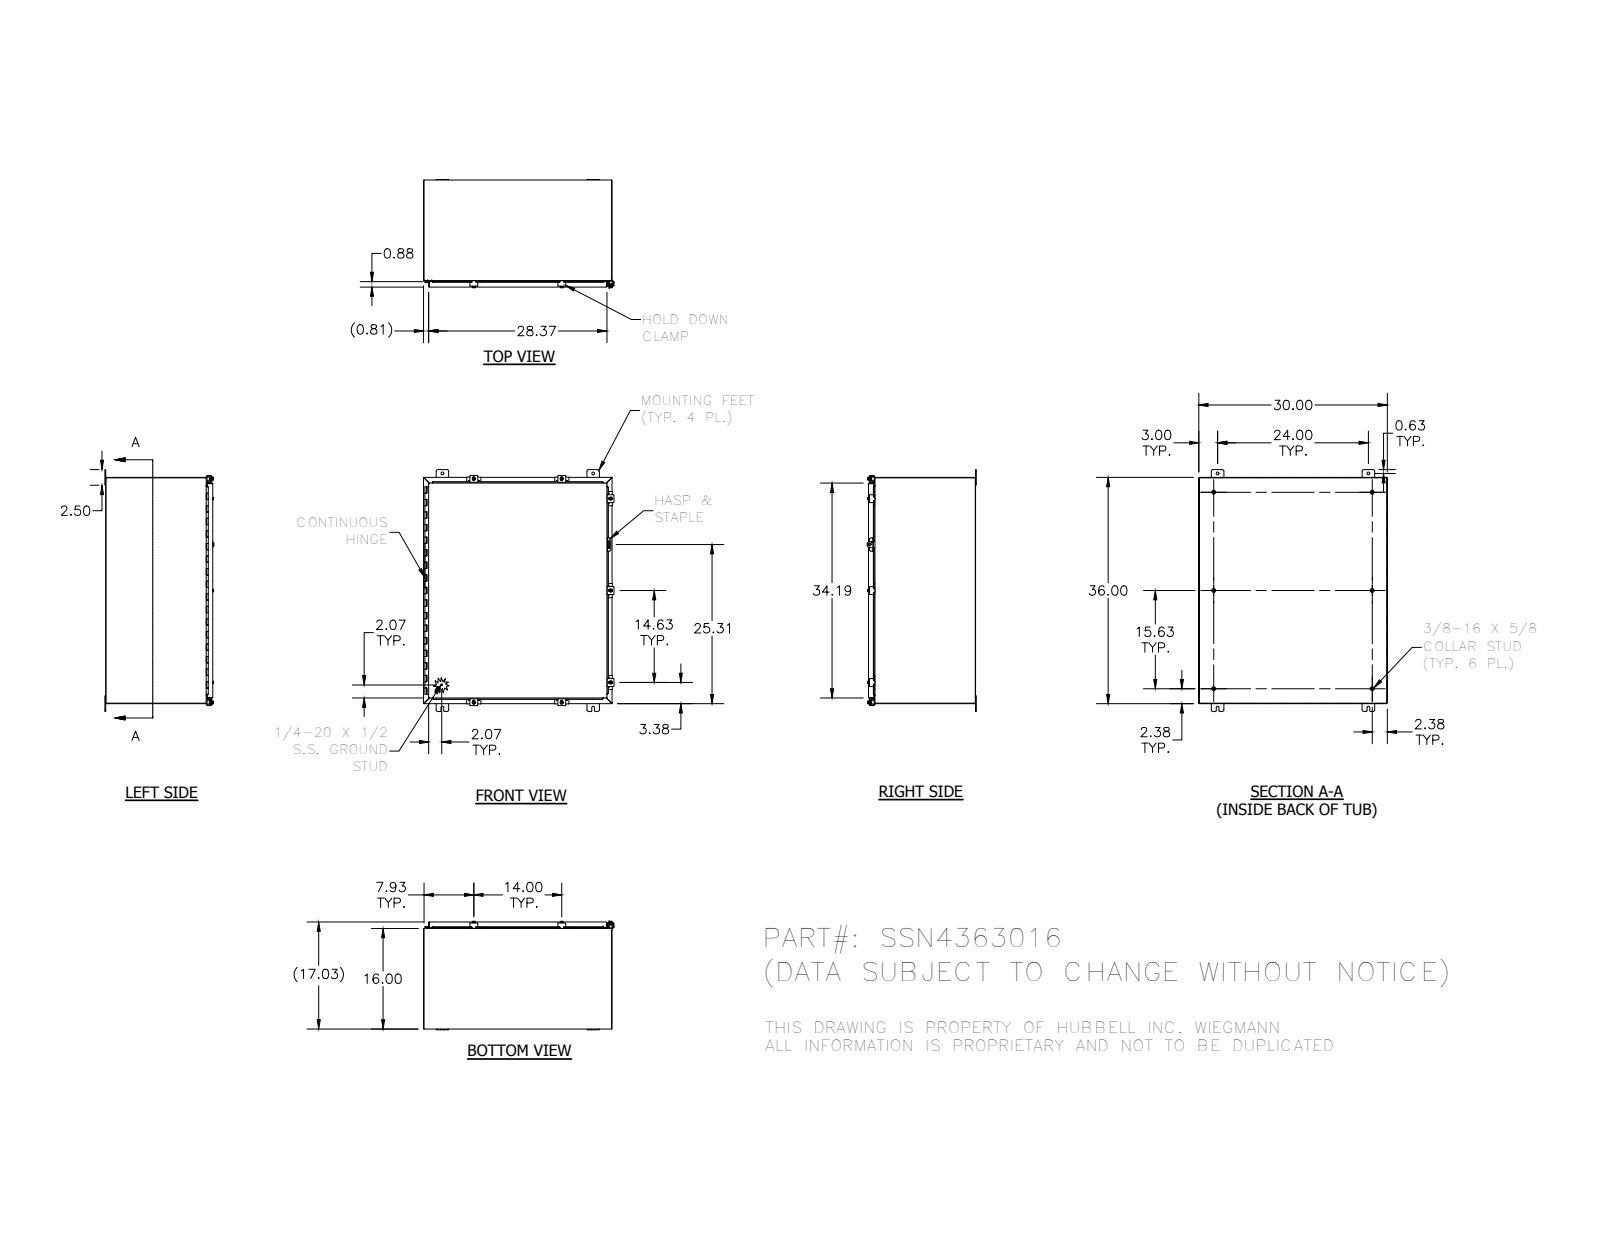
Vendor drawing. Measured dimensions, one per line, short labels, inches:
name: 32874-36L; 38846; 30824-1; 32912 (+8 more)
written by: SolidWorks 2014 (AUTOMOTIVE_DESIGN)
unit: in
bodies: 56 solids, 2194 faces (876 planar, 943 cylindrical, 375 other)
size: 38.5 × 30.311 × 17.355
volume: 360.5 in³; area: 9 572 in²
holes: 17× ⌀0.11, 7× ⌀0.211, 7× ⌀0.281, 7× ⌀0.3, 4× ⌀0.438, 1× ⌀0.125, 1× ⌀0.156, 1× ⌀0.5
bosses: 9× ⌀0.25, 7× ⌀0.52, 7× ⌀0.5, 7× ⌀0.35, 6× ⌀0.625, 6× ⌀0.33, 1× ⌀0.337, 1× ⌀0.12
rounds: 83× R0.03, 37× R0.125, 33× R0.25, 21× R0.031, 21× R0.105, 14× R0.062, 14× R0.141, 10× R0.1
face distances: 0.074, 16.959, 29.926, 16.885, 17.033, 35.926, 29.852, 30, 35.852, 36
hole spacings: 0.876, 35.298, 14, 1.625, 0.876, 7.556, 8.433, 9.082
